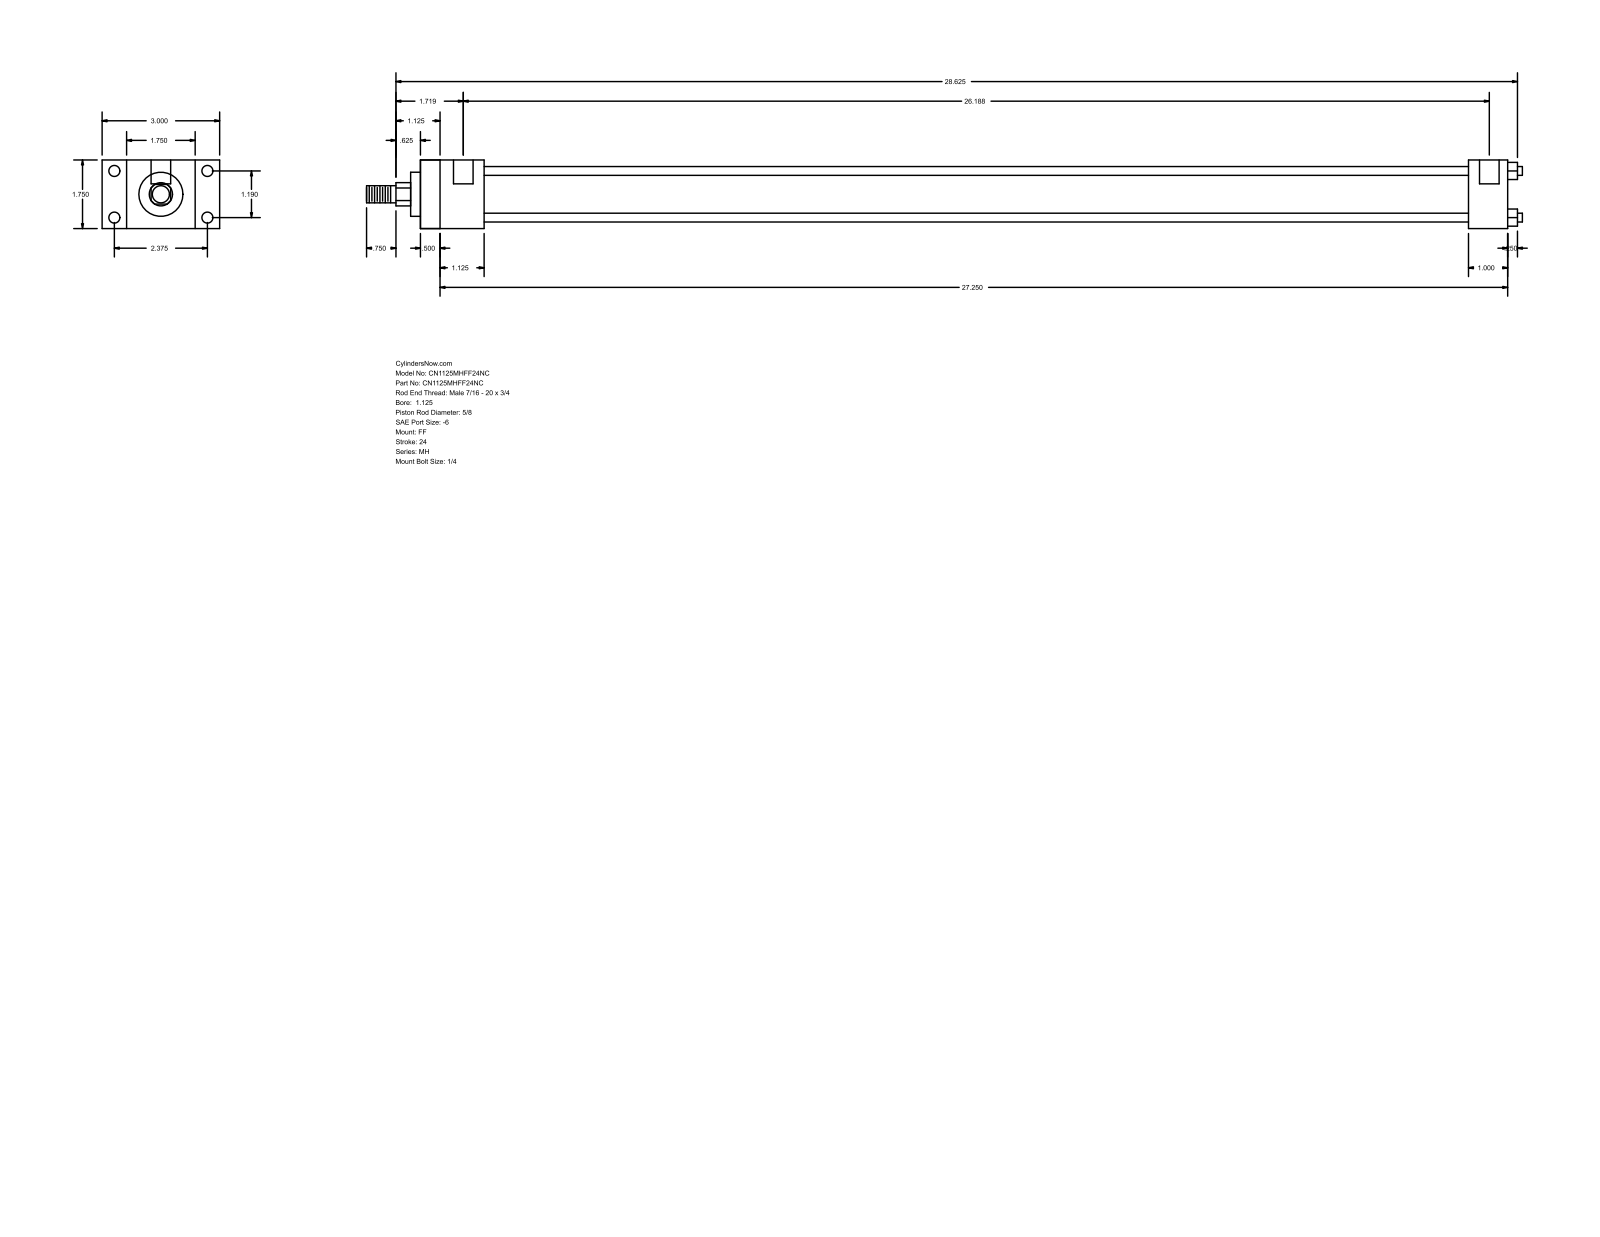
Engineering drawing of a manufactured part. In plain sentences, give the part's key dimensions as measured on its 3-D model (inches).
The part is named "MH_FF__0112_0.625". Its 3-D file was written by "GSSL Pune (CONFIG_CONTROL_DESIGN)". It is 0 solids with 92 faces: 64 planar, 28 cylindrical and 0 other. Overall it measures 29.5 by 3 by 1.75 inches. Round holes: 4 of diameter 0.219, 4 of diameter 0.281, 2 of diameter 0.5. Round bosses or shafts: 4 of diameter 0.225, 1 of diameter 1.375, 1 of diameter 1.125, 1 of diameter 0.625, 1 of diameter 0.437. Partial cylindrical surfaces (rounded edges, fillets, slot ends): 1 of radius 0.297. The main face-to-face distances are 1.75, 27.75, 0.625, 0.5, 27.25, 1.125, 2.375, 1, 1.625, 26.75. The hole center spacings are 1.19, 2.375, 2.656, 26.063, 0.125, 26.187.
